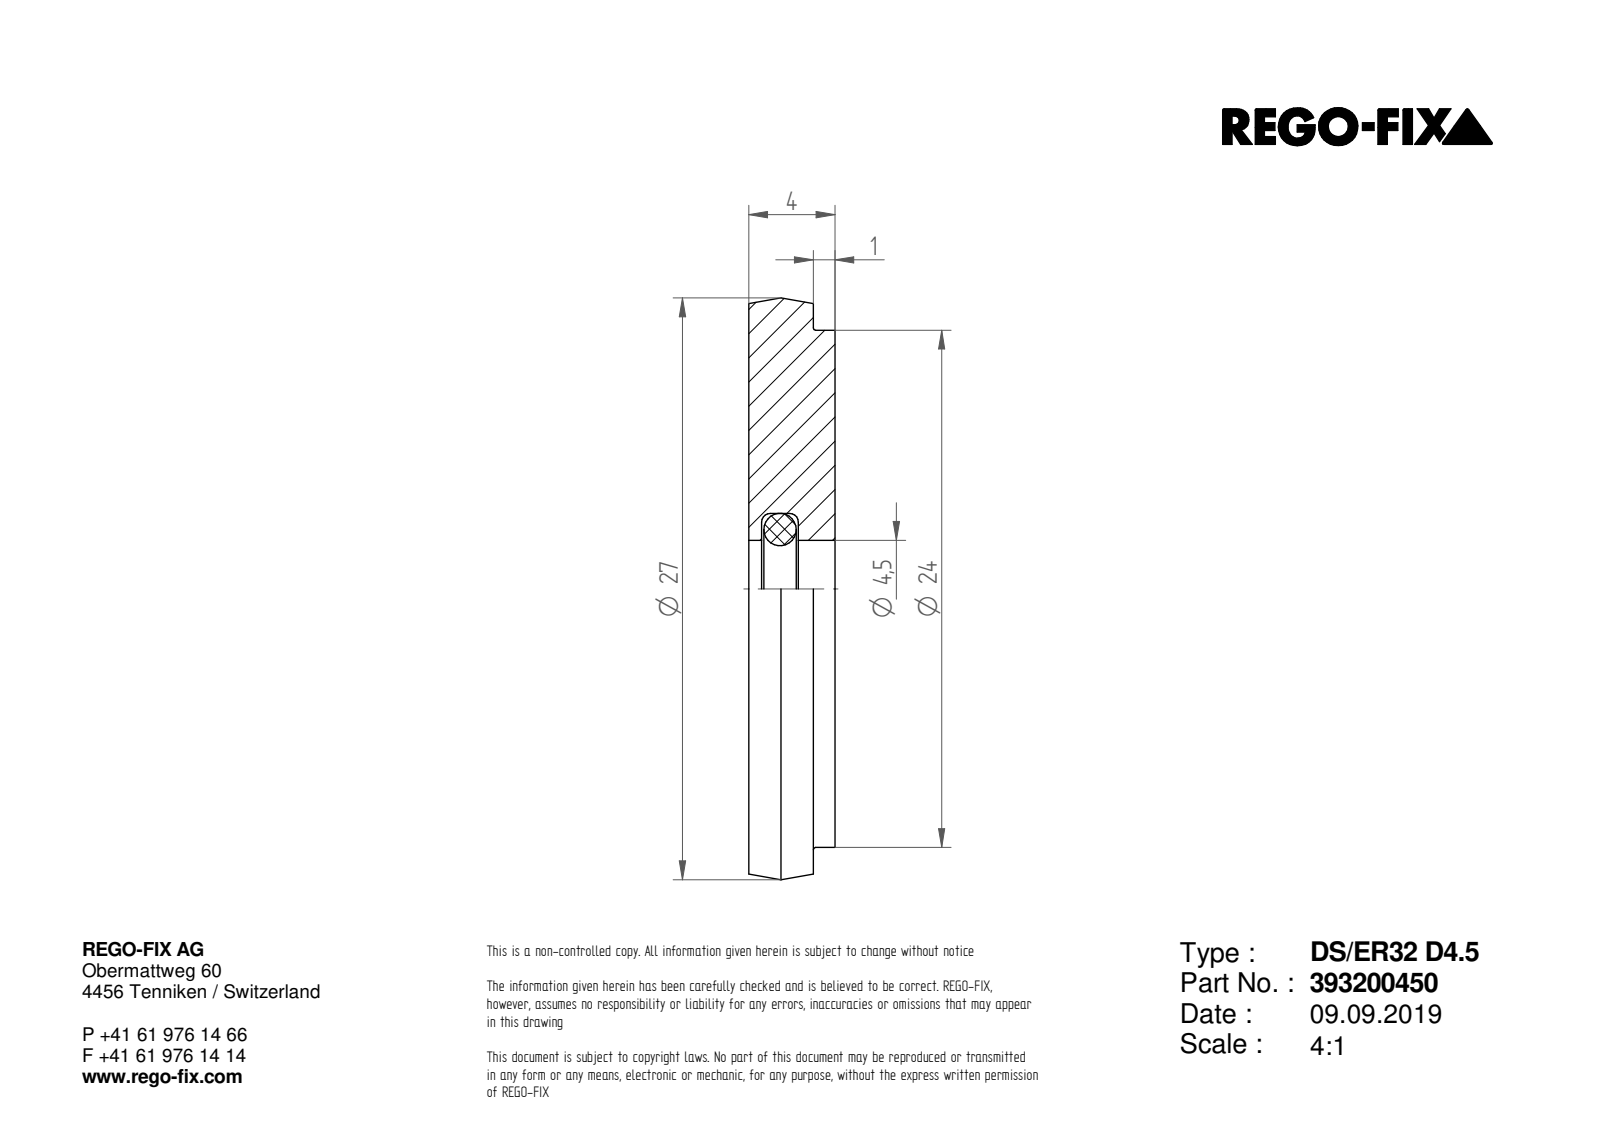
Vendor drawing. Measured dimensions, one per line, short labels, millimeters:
name: NOCUT
written by: SIEMENS PLM Software Solid Edge ST10 (AUTOMOTIVE_DESIGN)
unit: mm
bodies: 1 solid, 7 faces (3 planar, 3 cylindrical, 1 other)
size: 27 × 27 × 4
volume: 2 107 mm³; area: 1 496 mm²
holes: 1× ⌀4.5
bosses: 1× ⌀27, 1× ⌀24
face distances: 4, 1, 3
